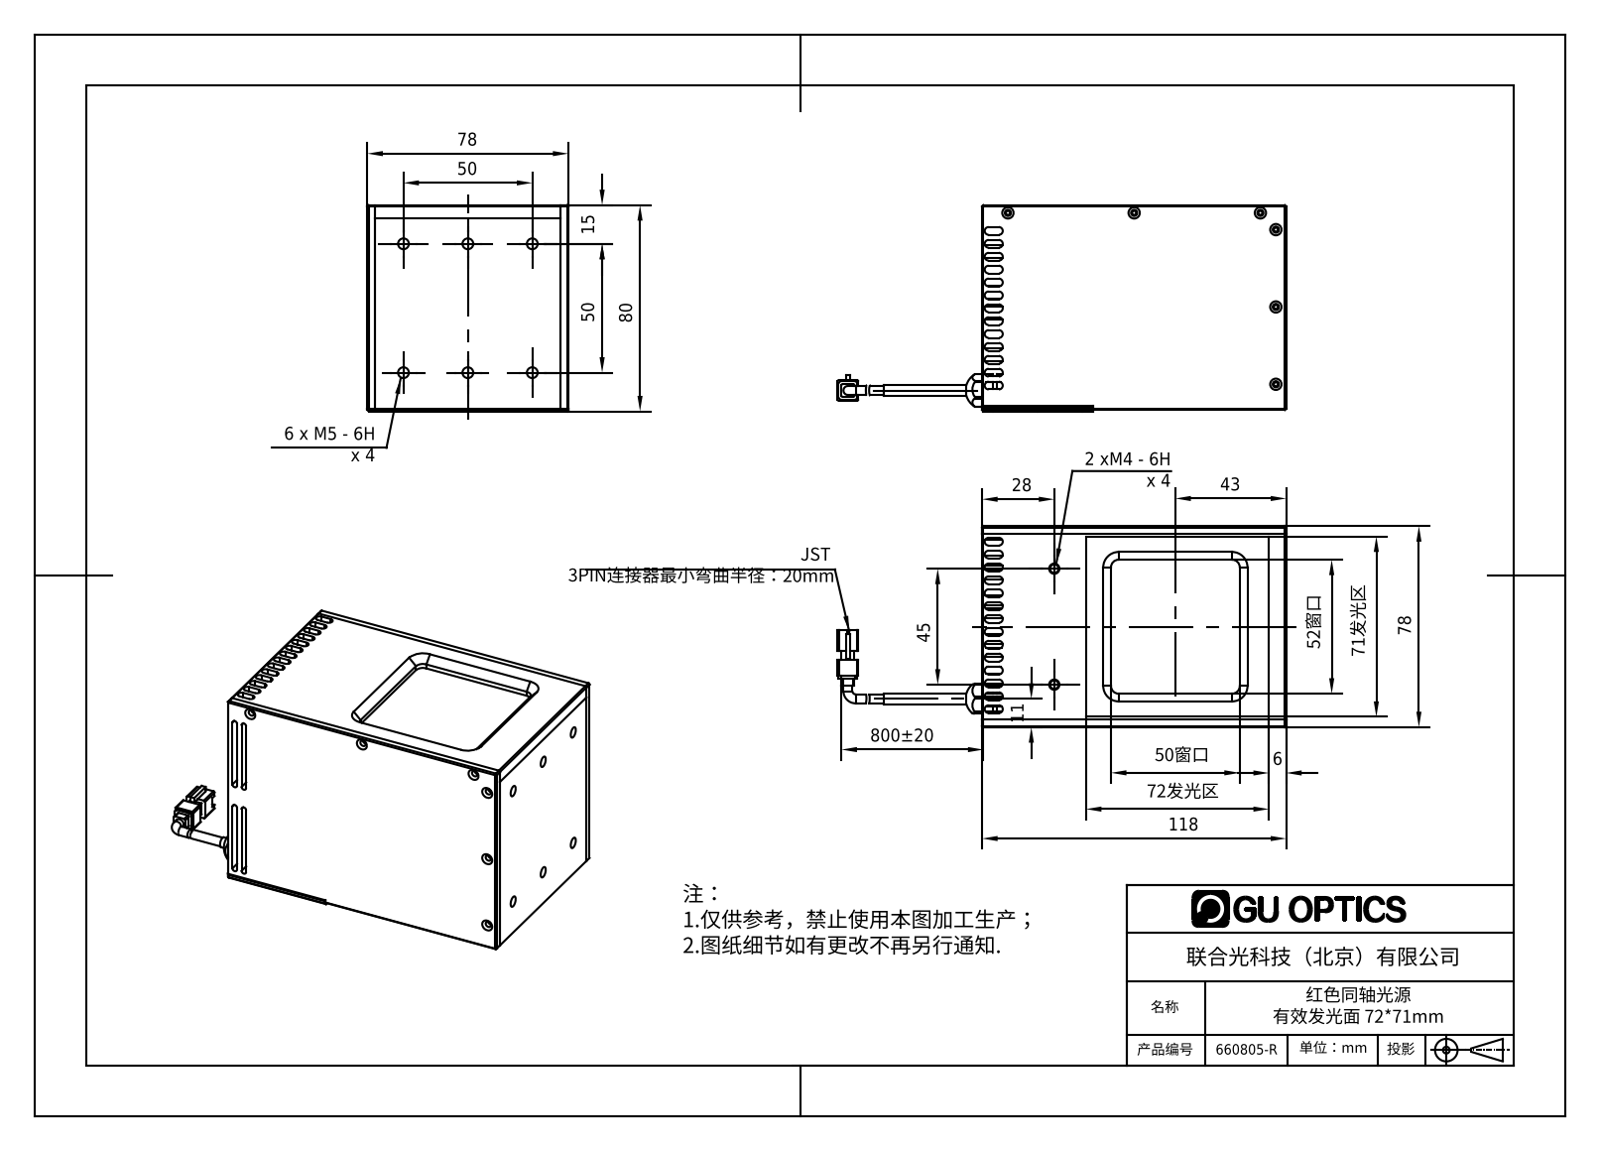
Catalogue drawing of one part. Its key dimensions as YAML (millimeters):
part_name: "红色同轴光源 有效发光面 7271mm"
step_written_by: "SolidWorks 2016 (AUTOMOTIVE_DESIGN)"
units: millimeters
bodies: {solids: 23, faces: 1600, planar: 1165, cylindrical: 278, other: 157}
overall_size: [151.44, 80.2, 78]
volume: 196586
surface_area: 164600
round_holes:
  - {diameter: 2.4, count: 16}
  - {diameter: 1.6, count: 15}
  - {diameter: 2, count: 9}
  - {diameter: 4.2, count: 6}
  - {diameter: 7, count: 4}
  - {diameter: 3.8, count: 1}
  - {diameter: 6.8, count: 1}
  - {diameter: 9, count: 1}
round_bosses_or_shafts:
  - {diameter: 3.5, count: 2}
  - {diameter: 9.76, count: 1}
  - {diameter: 8, count: 1}
  - {diameter: 4, count: 1}
partial_cylinders:
  - {radius: 1.5, count: 54}
  - {radius: 1, count: 12}
  - {radius: 0.5, count: 8}
  - {radius: 2, count: 4}
  - {radius: 3, count: 4}
  - {radius: 0.8, count: 1}
  - {radius: 6.25, count: 1}
face_to_face_distances: [1, 4, 74, 6, 75, 78, 100, 3, 2, 70]
hole_center_spacings: [50, 17.5, 25, 55.9, 75.07, 70, 73, 1.1]
